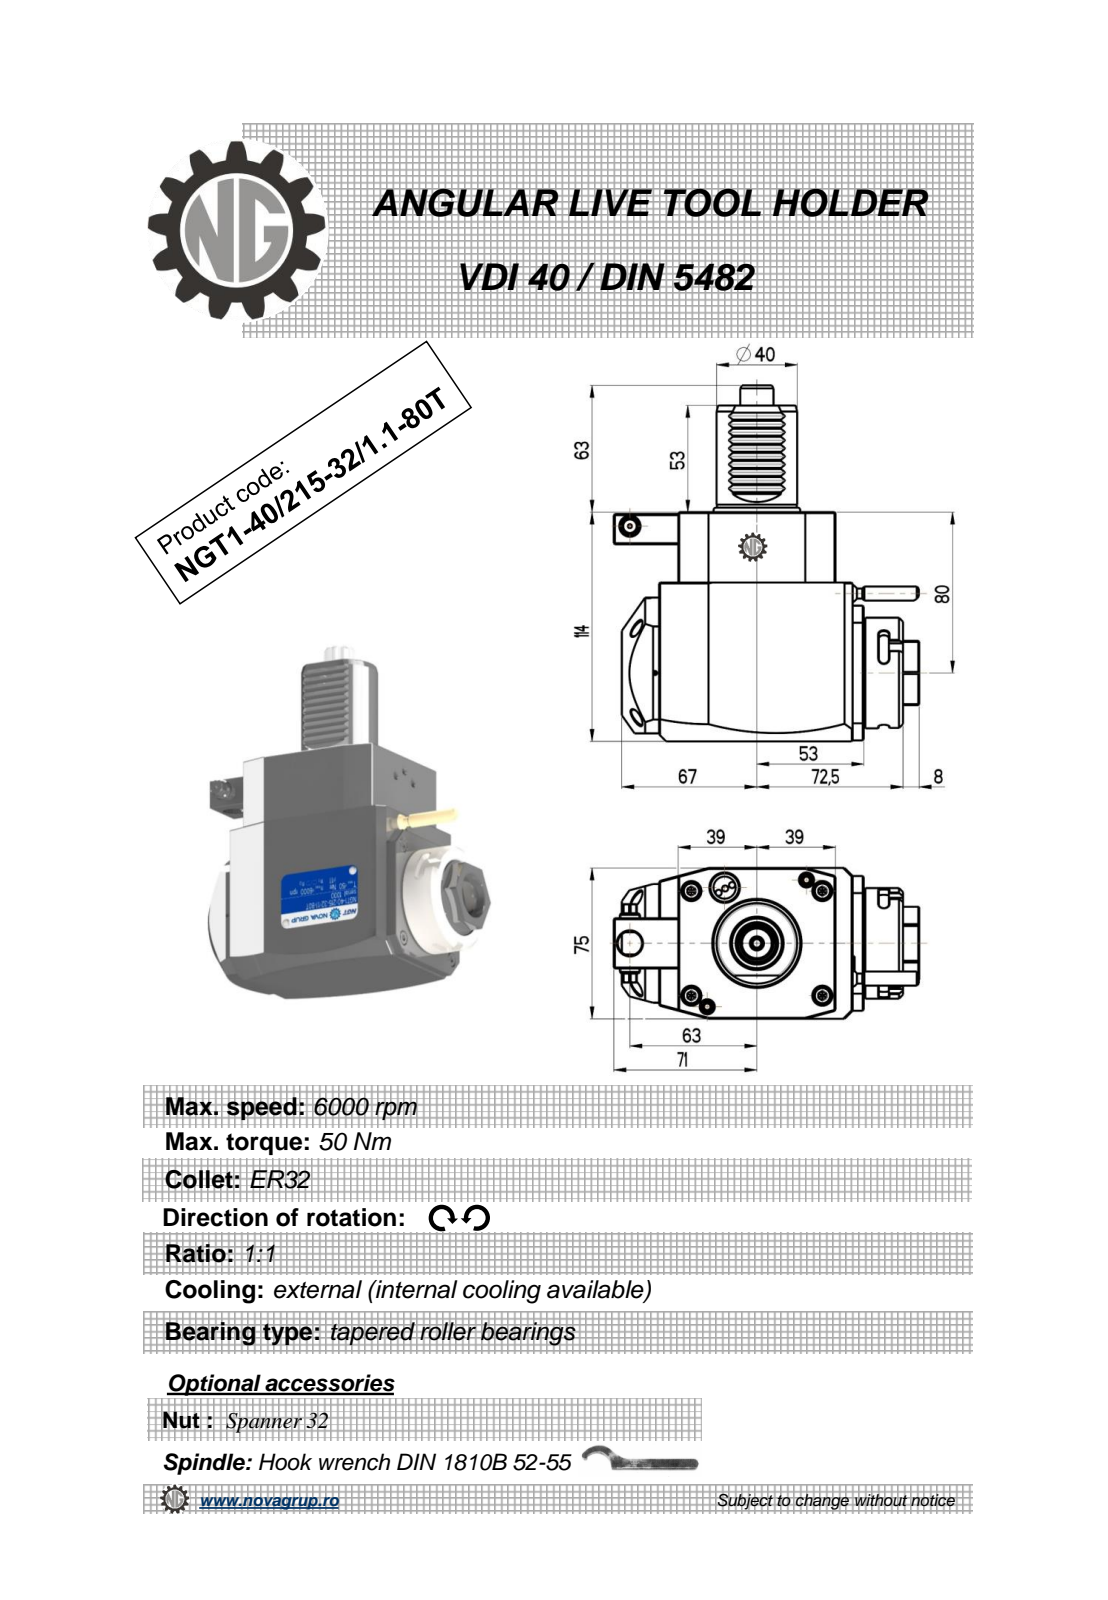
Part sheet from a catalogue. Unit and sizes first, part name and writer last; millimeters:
Units: millimetres
Overall size (bounding box): 177 × 151.5 × 75
Round holes (diameter × count): ⌀2 ×1, ⌀2.5 ×1, ⌀3 ×1, ⌀4.2 ×1, ⌀4.5 ×1, ⌀5.3 ×1, ⌀9.5 ×1, ⌀12 ×1, ⌀23 ×1
Round bosses / shafts (diameter × count): ⌀8 ×2, ⌀55 ×1, ⌀48 ×1, ⌀40 ×1, ⌀10 ×1, ⌀7 ×1, ⌀5 ×1, ⌀4 ×1
Partial cylindrical surfaces — rounded edges, fillets, slot ends (radius × count): R3.03 ×18, R0.3 ×10, R2.5 ×6, R180 ×2, R0.5 ×1, R3.85 ×1, R4.25 ×1, R6.75 ×1
Main face-to-face distances: 75, 114, 14, 78, 92, 25, 111.5, 33.5, 19.5, 4
Hole centre spacings: 37.35, 43.2, 63, 72.5
Volume: 952 921 mm³ · Surface area: 71 237 mm²
Bodies: 1 solid, 397 faces (183 planar, 121 cylindrical, 93 other)
Part name (STEP PRODUCT): NGT1_40_215_32_1_1_80T
STEP written by: PRO/ENGINEER BY PARAMETRIC TECHNOLOGY CORPORATION, 2010280 (CONFIG_CONTROL_DESIGN)
